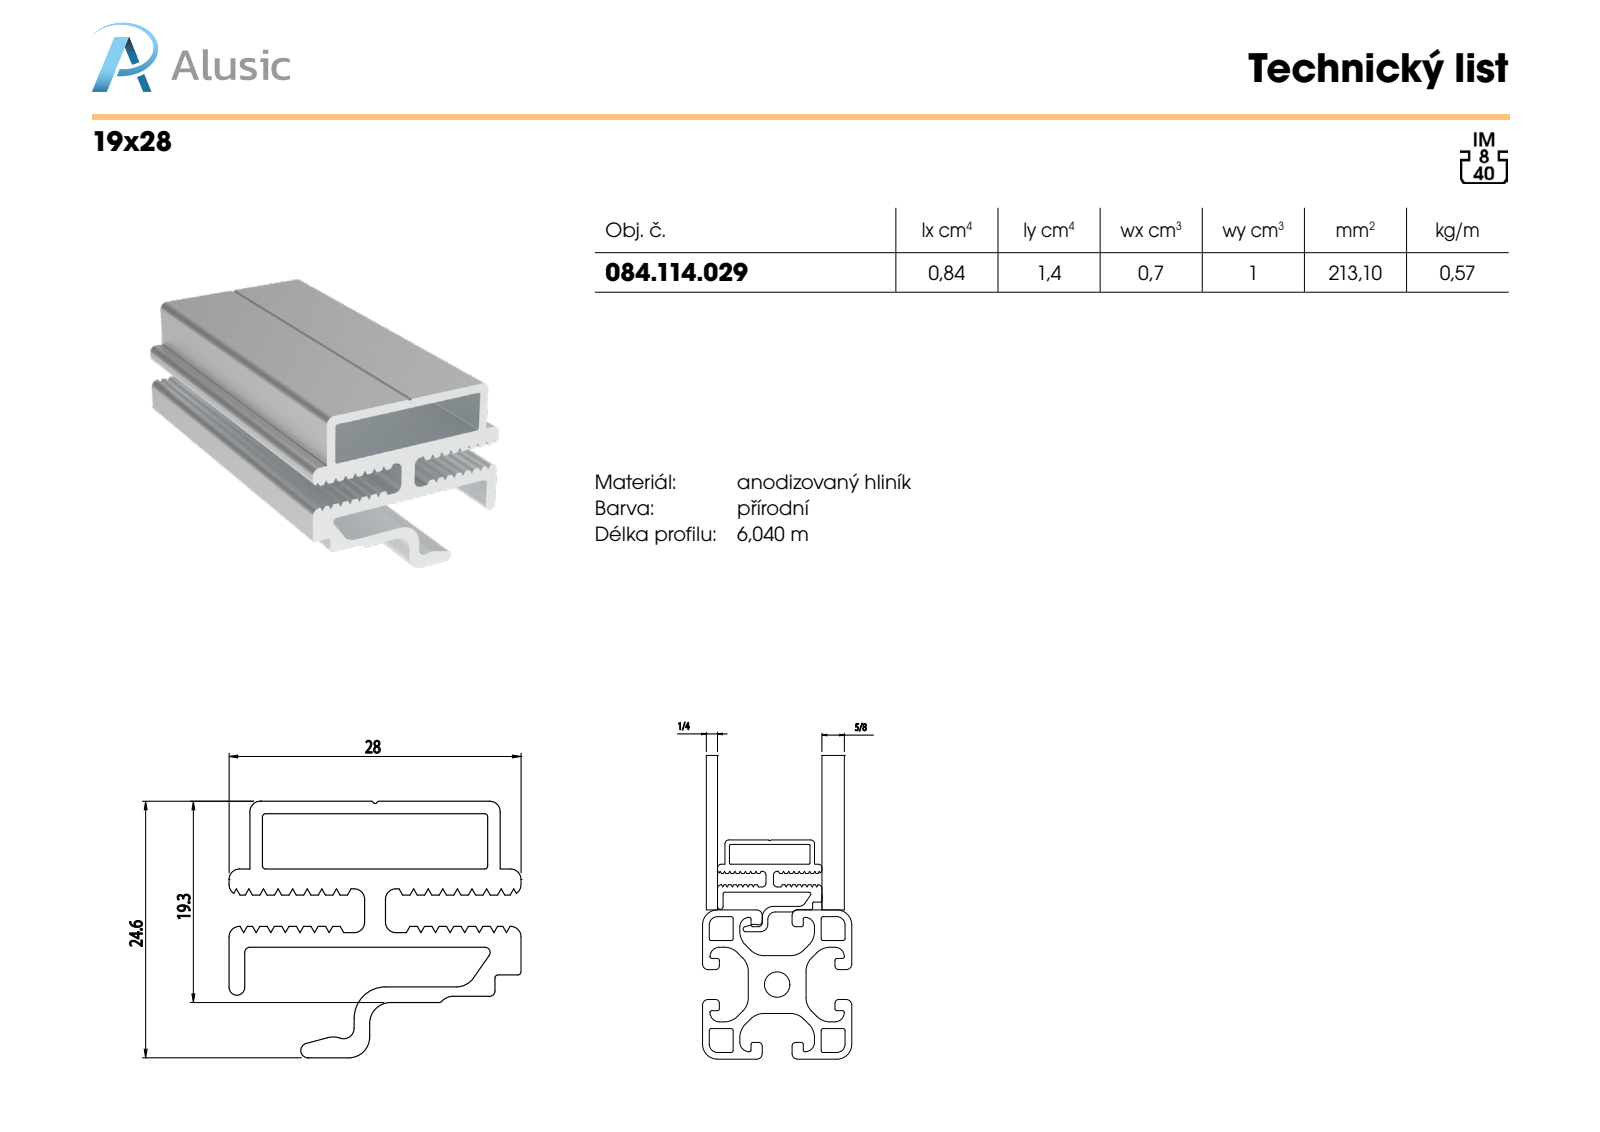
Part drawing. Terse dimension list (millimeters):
name: 084.114.029
written by: SolidWorks 2018 (AUTOMOTIVE_DESIGN)
unit: mm
bodies: 1 solid, 165 faces (132 planar, 33 cylindrical, 0 other)
size: 100 × 28 × 24.6
volume: 21 310 mm³; area: 27 157 mm²
rounds: 13× R1, 7× R0.3, 4× R2, 3× R0.5, 1× R0.2, 1× R0.7, 1× R0.75, 1× R1.5
face distances: 1.2, 5.3, 12.8, 7.5, 14, 6.5, 2, 1.21, 2.5, 12
